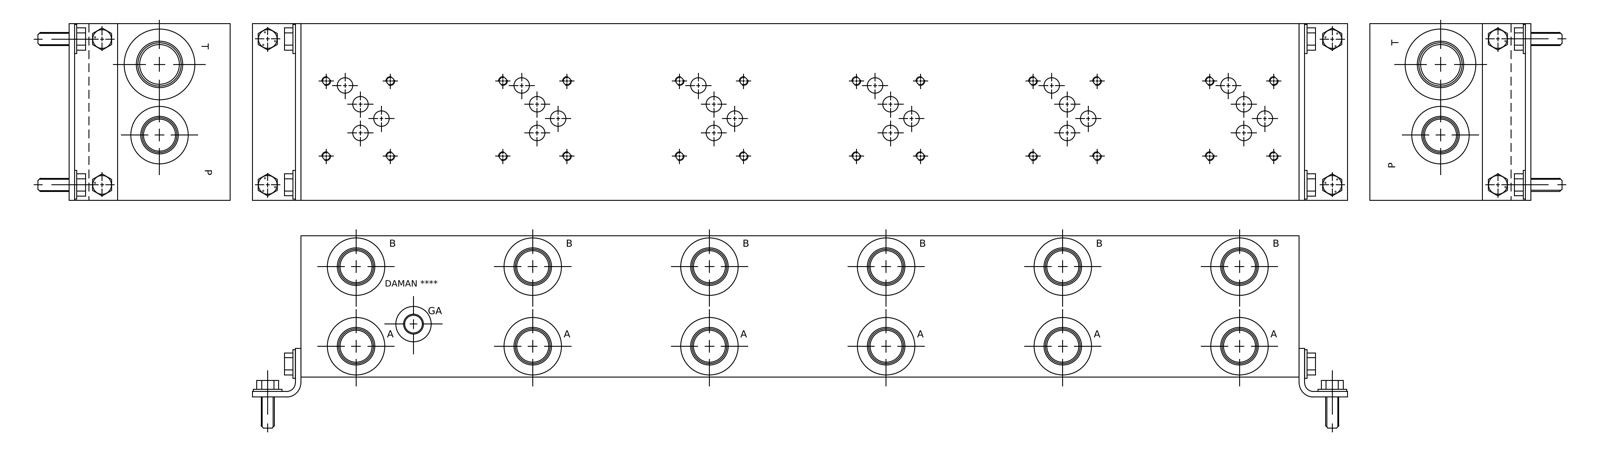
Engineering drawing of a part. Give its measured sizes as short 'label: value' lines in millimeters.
name: Part_AD05HP065S_3D
written by: Autodesk Inventor 2020 (AUTOMOTIVE_DESIGN)
unit: mm
bodies: 1 solid, 1008 faces (497 planar, 166 cylindrical, 345 other)
size: 717.55 × 127 × 101.6
volume: 8 910 000 mm³; area: 413 989 mm²
holes: 24× ⌀5.11, 24× ⌀6.35, 22× ⌀11.13, 13× ⌀23.01, 13× ⌀24.92, 13× ⌀27.43, 13× ⌀42.04, 12× ⌀27, 2× ⌀7.92, 2× ⌀9.53, 2× ⌀11.11, 2× ⌀26.99
face distances: 101.6, 127, 0.79, 717.55, 126.21, 716.76, 19.05, 715.97, 19.84, 107.16
hole spacings: 127, 254, 381, 139.27, 508, 260.35, 17.49, 20.63
